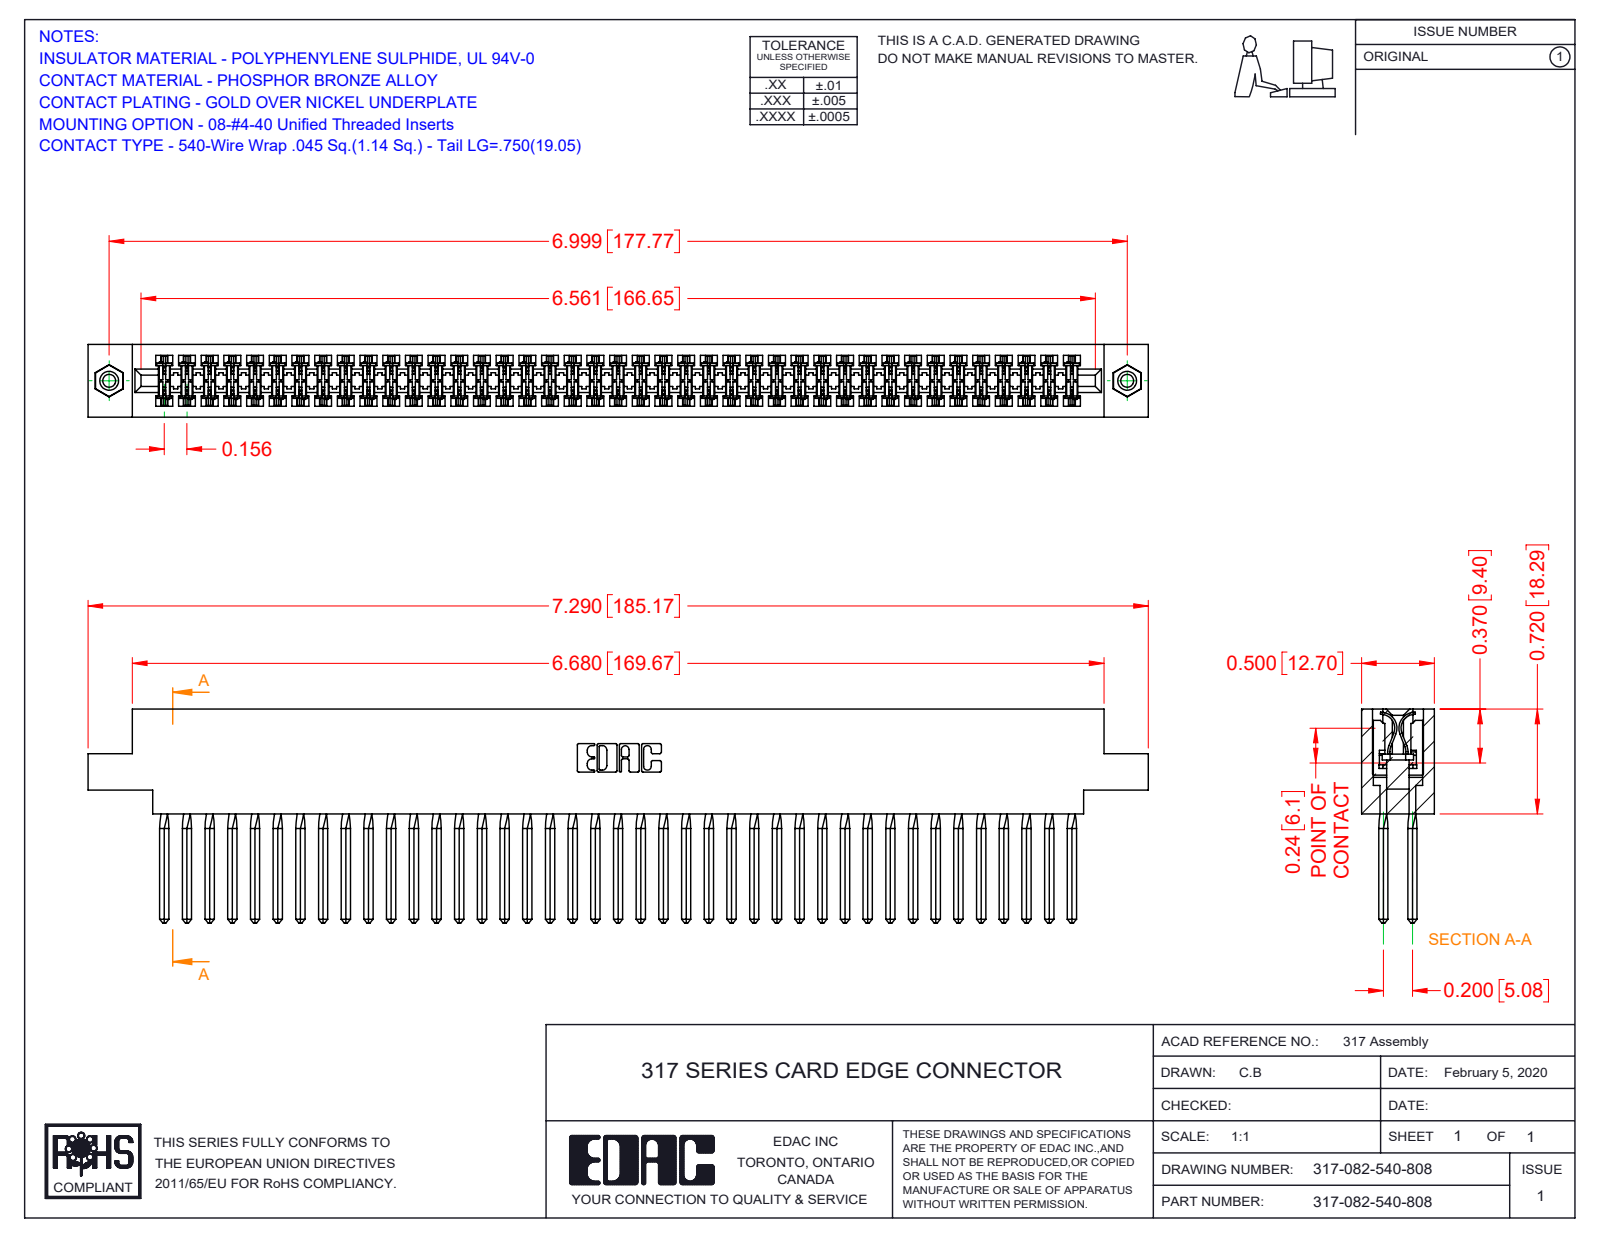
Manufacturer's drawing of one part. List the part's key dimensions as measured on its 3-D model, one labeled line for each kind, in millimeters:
Part name (STEP PRODUCT): 317 Part_.156 Dia - TI; 317-290-001_540; 345-250-001_345-250-003-102; 317-082-540-808
STEP written by: SolidWorks 2016 (CONFIG_CONTROL_DESIGN)
Units: millimetres
Bodies: 85 solids, 7460 faces (6076 planar, 1040 cylindrical, 344 other)
Overall size (bounding box): 185.2 × 37.3 × 12.7
Volume: 31 040 mm³ · Surface area: 46 260 mm²
Round holes (diameter × count): ⌀2.3 ×2, ⌀3.2 ×2, ⌀4 ×2
Round bosses / shafts (diameter × count): ⌀3.9 ×2
Partial cylindrical surfaces — rounded edges, fillets, slot ends (radius × count): R0.4 ×164, R0.3 ×22, R0.2 ×6, R0.8 ×6, R0.7 ×3, R2.4 ×2, R2.5 ×2, R2.8 ×2
Main face-to-face distances: 12.7, 1.9, 10.8, 8.9, 5, 2.4, 5.1, 2.9, 3.3, 1.2
Hole centre spacings: 177.8
